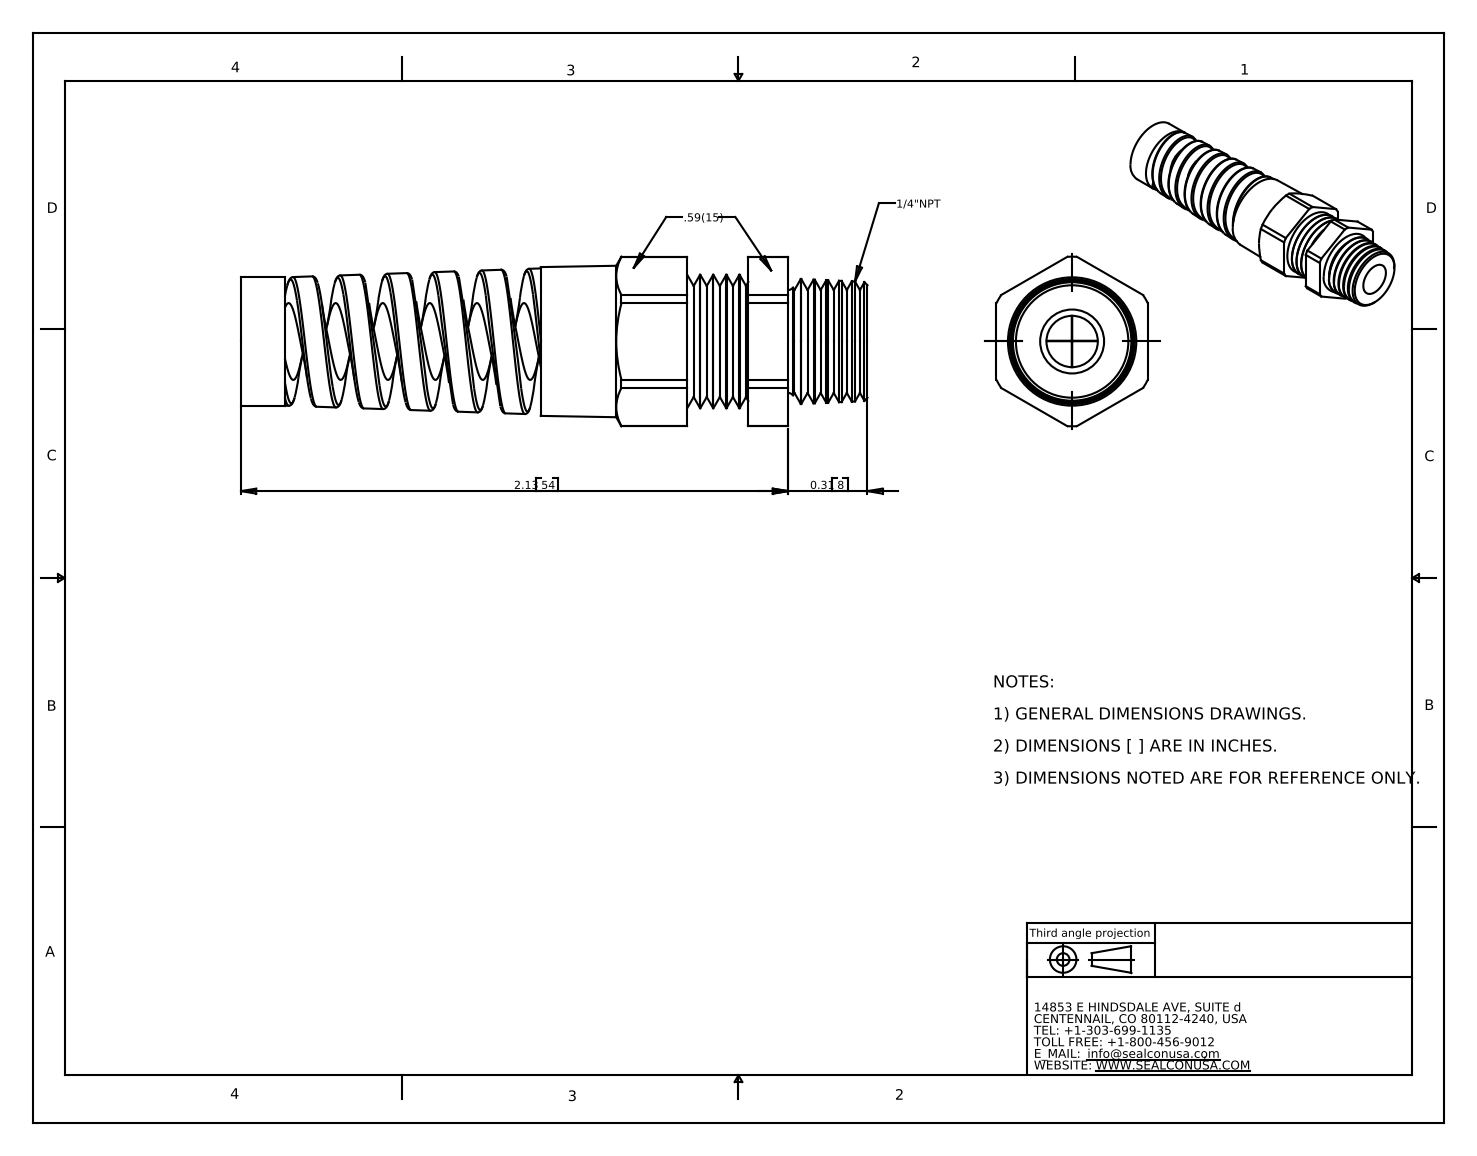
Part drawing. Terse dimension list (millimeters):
name: CF07AR-GY
written by: SolidWorks 2007 (CONFIG_CONTROL_DESIGN)
unit: mm
bodies: 1 solid, 146 faces (19 planar, 39 cylindrical, 88 other)
size: 62 × 16.8 × 15
volume: 5 830 mm³; area: 5 238 mm²
holes: 1× ⌀5.1, 1× ⌀7.6
bosses: 1× ⌀13.2, 1× ⌀12.7
rounds: 1× R8.4
face distances: 15, 29.6, 54.1, 24.5, 62, 32.3, 7.9, 50.2, 20.5, 3.9
